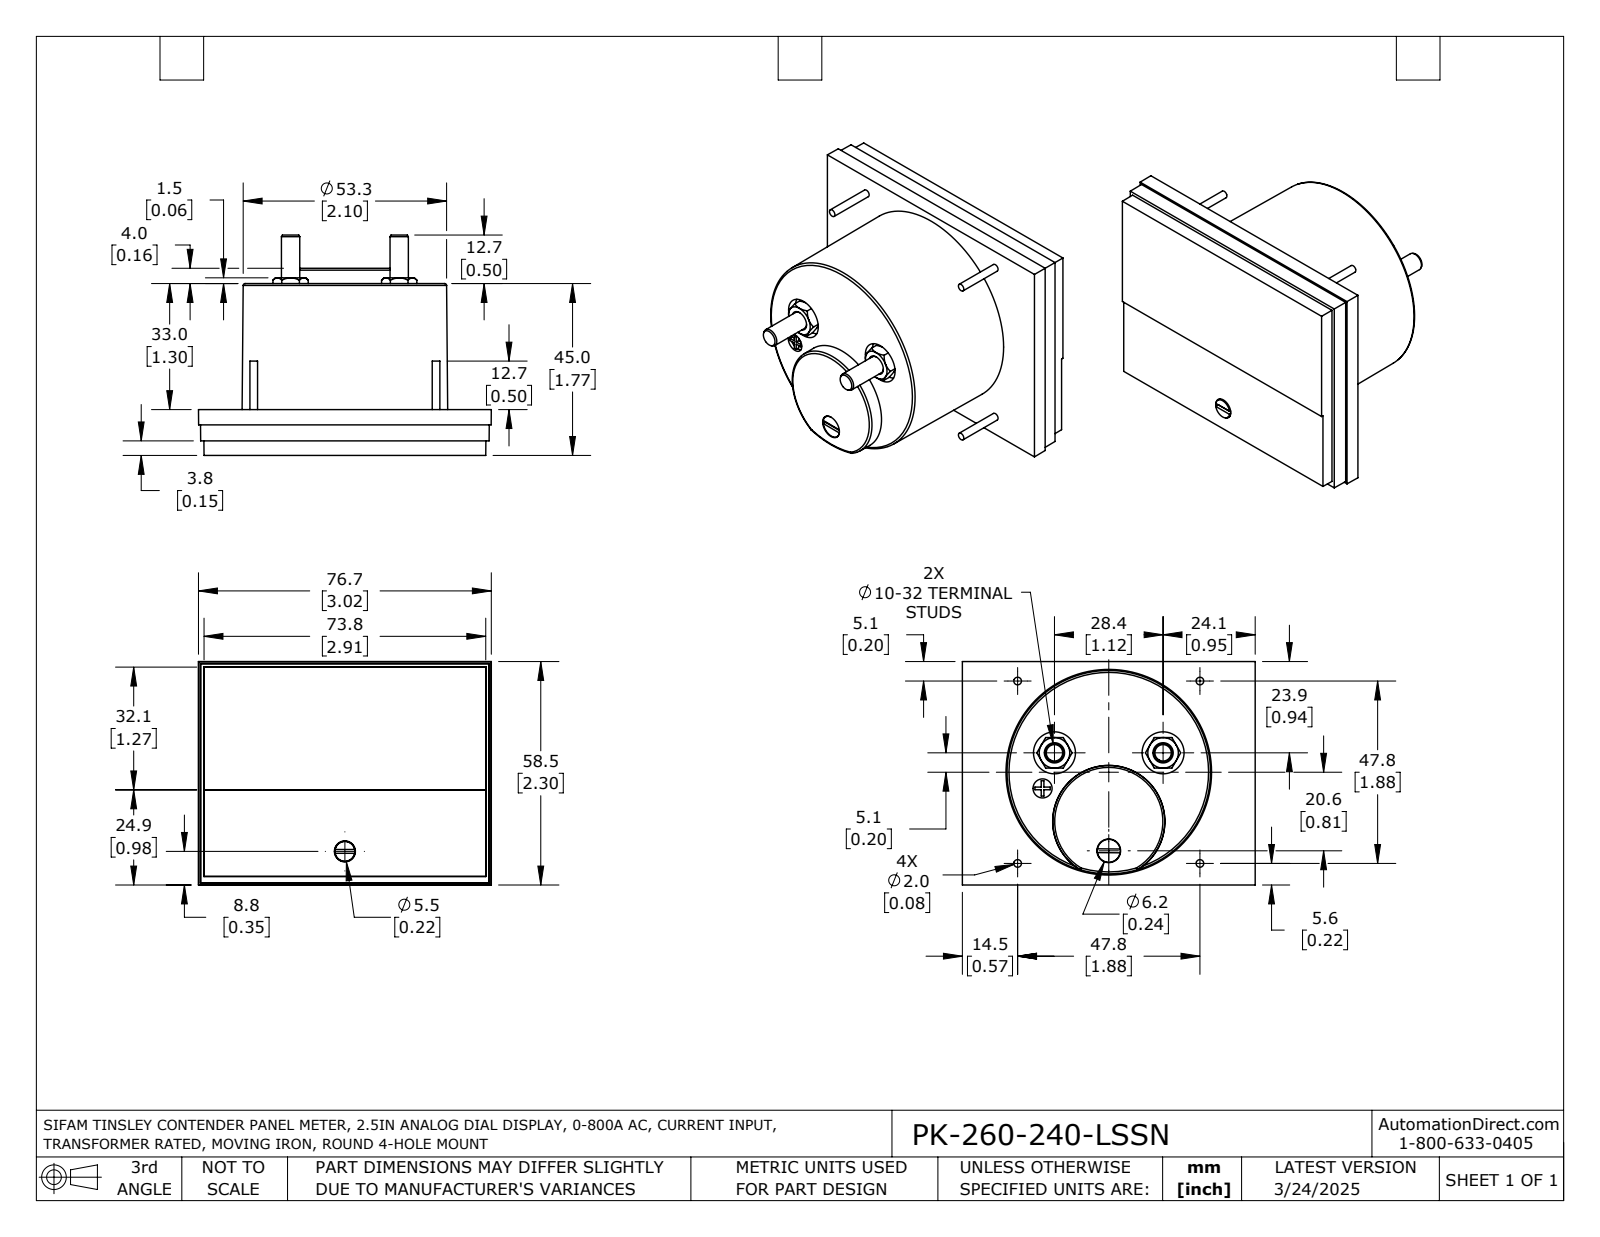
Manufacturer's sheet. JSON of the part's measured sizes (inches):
{"part_name": "PK-260-240-LSSN", "step_written_by": "SolidWorks 2021 (AUTOMOTIVE_DESIGN)", "units": "inches", "bodies": {"solids": 1, "faces": 192, "planar": 95, "cylindrical": 37, "other": 60}, "overall_size": [3.02, 2.303, 2.272], "volume_in3": 7.657, "surface_area_in2": 36.55, "round_holes": [[0.197, 3], [0.433, 2], [0.209, 1], [0.217, 1], [0.244, 1]], "round_bosses_or_shafts": [[0.079, 4], [0.189, 2], [0.236, 1], [0.205, 1]], "partial_cylinders_radius": [[0.033, 1]], "face_to_face_distances": [0.02, 0.472, 0.13, 0.322, 0.15, 0.453, 0.057, 0.077, 0.396, 0.073], "hole_center_spacings": [1.155, 1.16, 0.387, 0.938, 0.942, 1.12, 1.295]}
